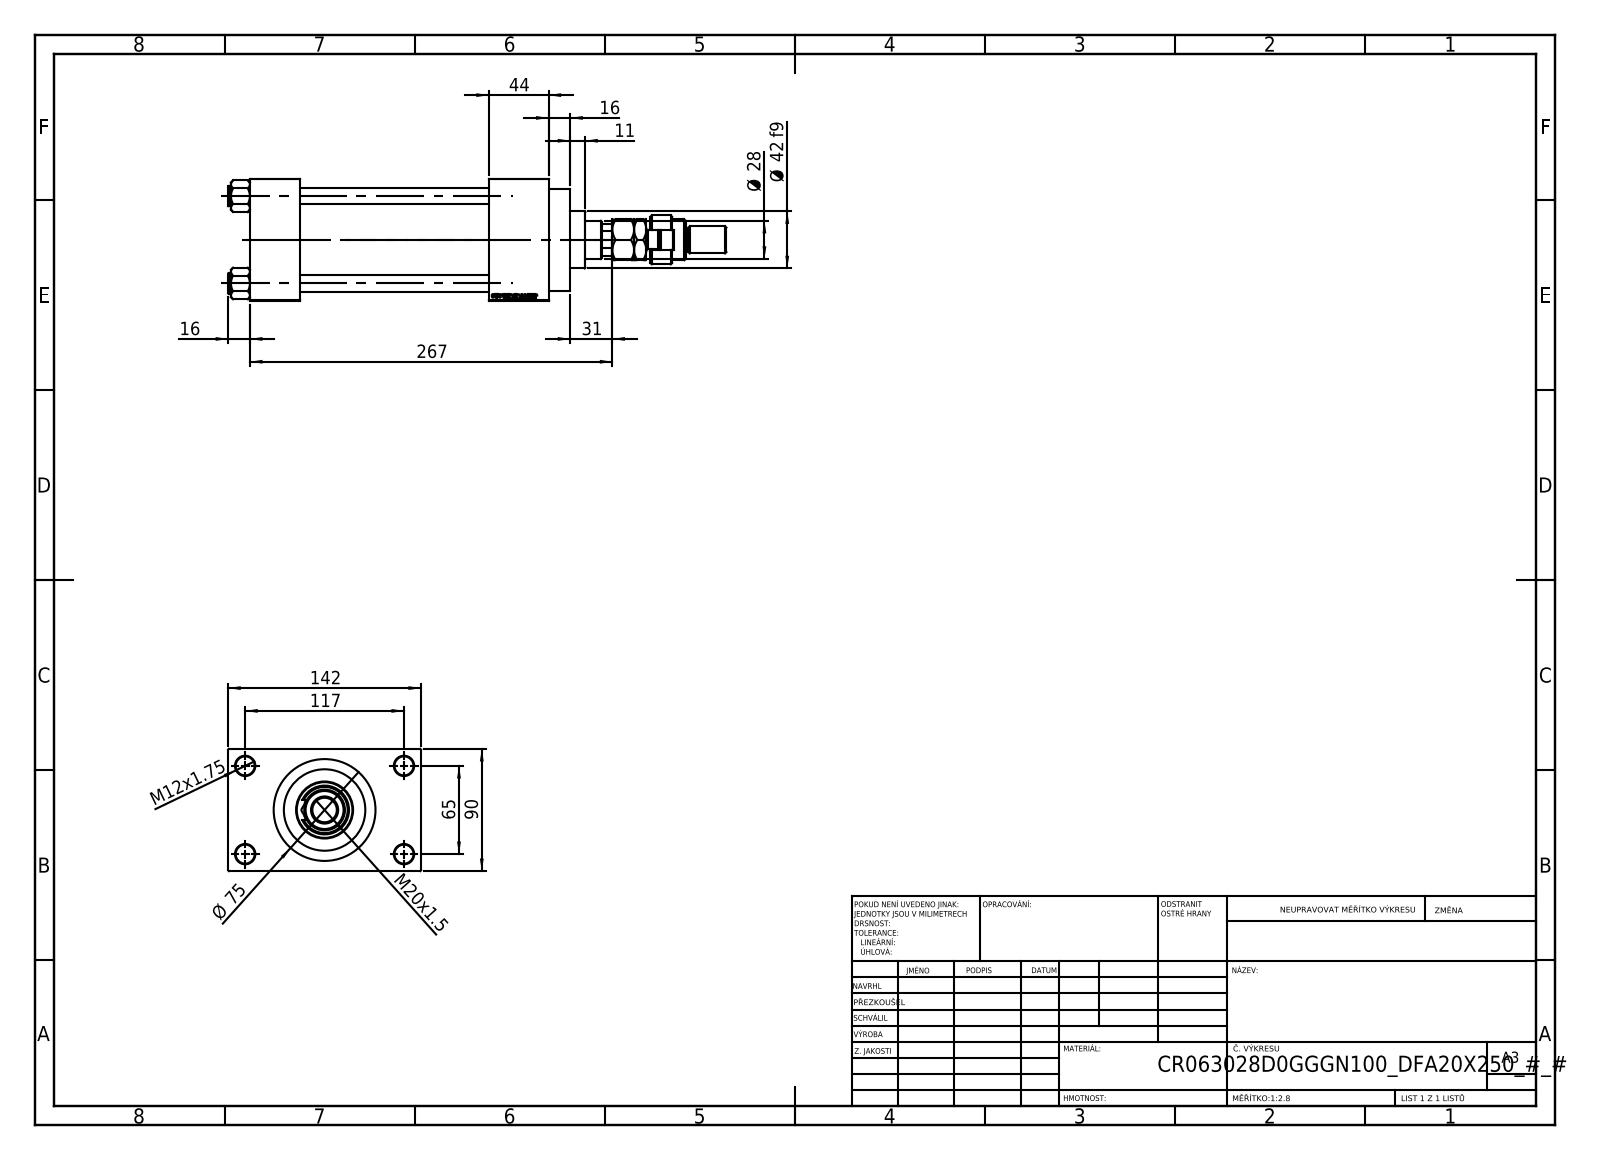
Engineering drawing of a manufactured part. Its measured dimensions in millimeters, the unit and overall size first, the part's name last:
Units: millimetres
Overall size (bounding box): 367 × 142 × 90
Round holes (diameter × count): ⌀12 ×4, ⌀14 ×4, ⌀7 ×2, ⌀20.96 ×2, ⌀30 ×2, ⌀18.5 ×1, ⌀28 ×1, ⌀31 ×1, ⌀50 ×1, ⌀60 ×1, ⌀63 ×1
Round bosses / shafts (diameter × count): ⌀15 ×4, ⌀75 ×1, ⌀69 ×1, ⌀42 ×1, ⌀36 ×1, ⌀30 ×1, ⌀22 ×1, ⌀20 ×1
Partial cylindrical surfaces — rounded edges, fillets, slot ends (radius × count): R7.5 ×1, R12 ×1, R13.5 ×1
Main face-to-face distances: 90, 139, 37, 176, 44, 220, 183, 116, 26, 142
Hole centre spacings: 26.35, 45.47, 64.3, 66.92, 69.81, 90.65, 111.34, 65
Volume: 1 289 000 mm³ · Surface area: 264 126 mm²
Bodies: 13 solids, 1189 faces (525 planar, 102 cylindrical, 562 other)
Part name (STEP PRODUCT): MFA; V215CR_D_TYCINKA; V215_VC_A; FEMALE_PART_FOR_DFA (+3 more)
STEP written by: SolidWorks 2019 (CONFIG_CONTROL_DESIGN)
